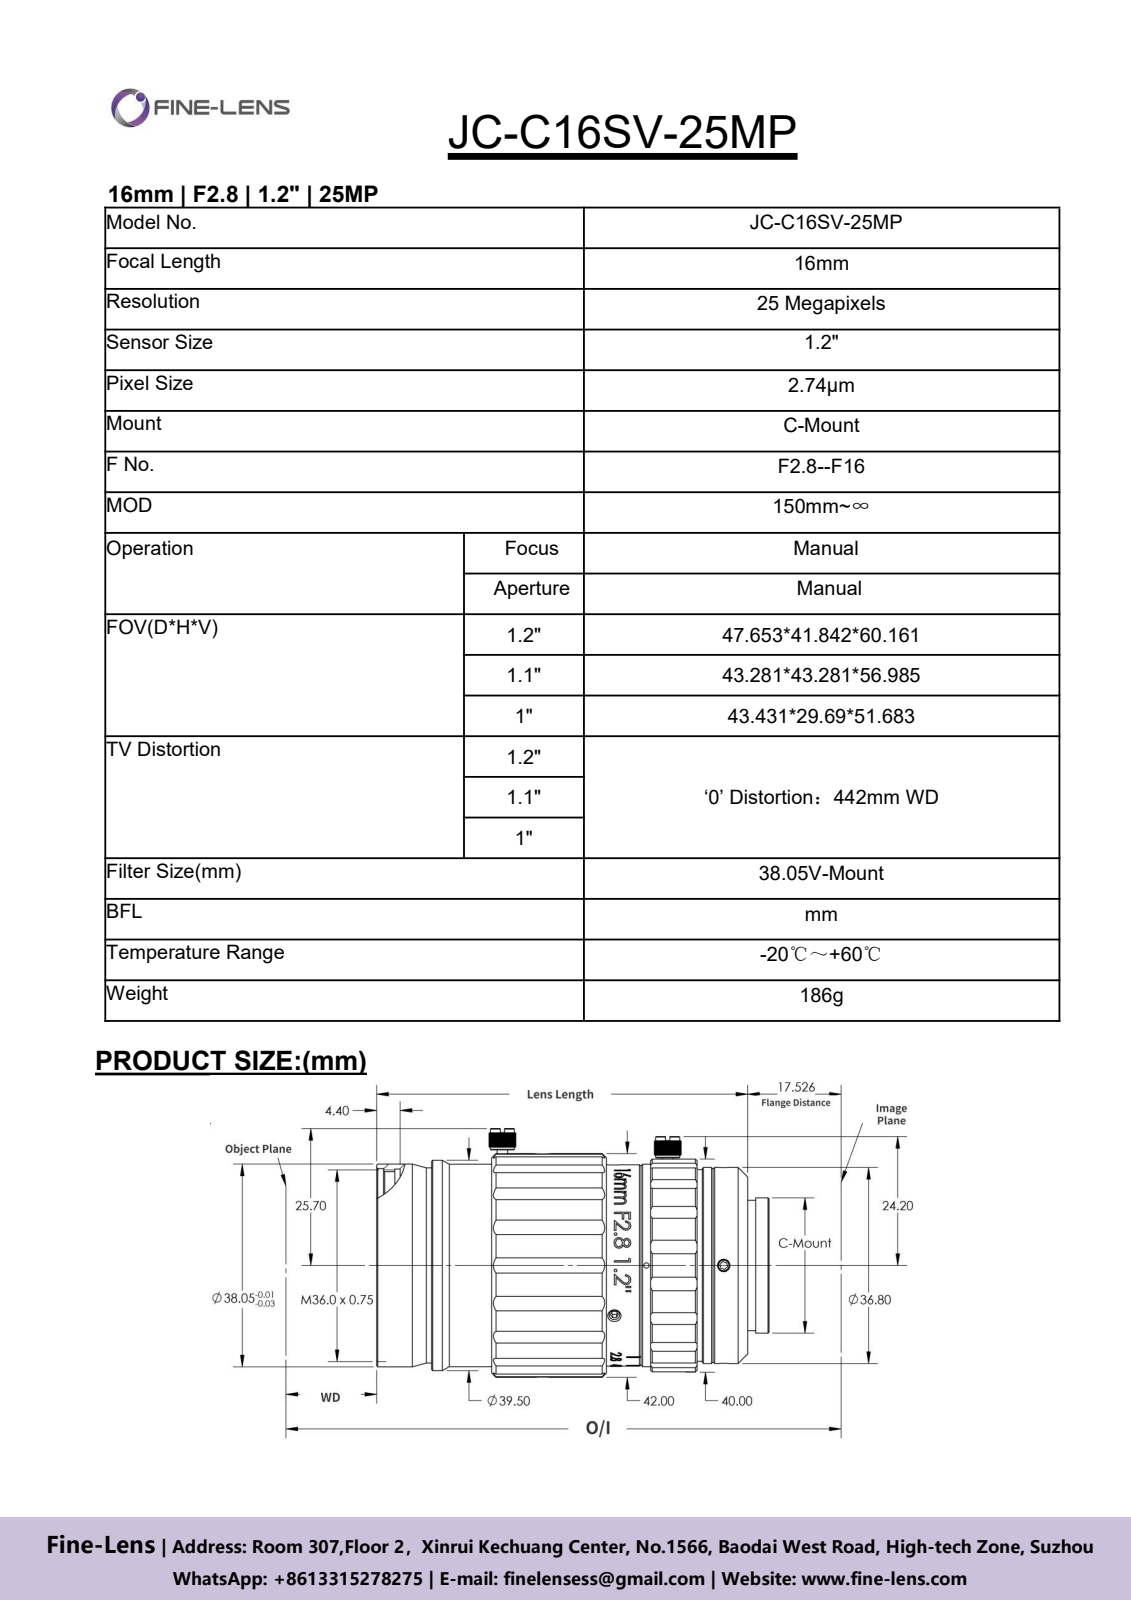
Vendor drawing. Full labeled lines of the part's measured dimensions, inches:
Part name (STEP PRODUCT): M2.5x3 平头顶丝; 16mmF28_1_2_3D; КЦВЦ
STEP written by: SolidWorks 2018 (CONFIG_CONTROL_DESIGN)
Units: inches
Bodies: 12 solids, 1621 faces (549 planar, 420 cylindrical, 652 other)
Overall size (bounding box): 2.876 × 1.965 × 1.626
Volume: 4.249 in³ · Surface area: 43.73 in²
Round holes (diameter × count): ⌀0.079 ×7, ⌀0.063 ×3, ⌀0.039 ×1, ⌀0.114 ×1, ⌀0.118 ×1, ⌀0.886 ×1, ⌀1.201 ×1, ⌀1.248 ×1, ⌀1.26 ×1, ⌀1.388 ×1, ⌀1.425 ×1, ⌀1.433 ×1
Round bosses / shafts (diameter × count): ⌀0.079 ×3, ⌀0.177 ×2, ⌀0.098 ×2, ⌀1.555 ×1, ⌀1.498 ×1, ⌀1.496 ×1, ⌀1.488 ×1, ⌀1.449 ×1
Partial cylindrical surfaces — rounded edges, fillets, slot ends (radius × count): R0.098 ×38, R0.049 ×4, R0.059 ×2, R0.079 ×2, R0.039 ×1, R0.746 ×1, R0.787 ×1, R0.815 ×1
Main face-to-face distances: 2.468, 0.689, 0.276, 0.039, 0.965, 1.779, 0.157, 1.503, 2.546, 1.043
Hole centre spacings: 0.787, 0.142, 0.154, 0.295, 0.393, 0.394, 0.531, 0.685
